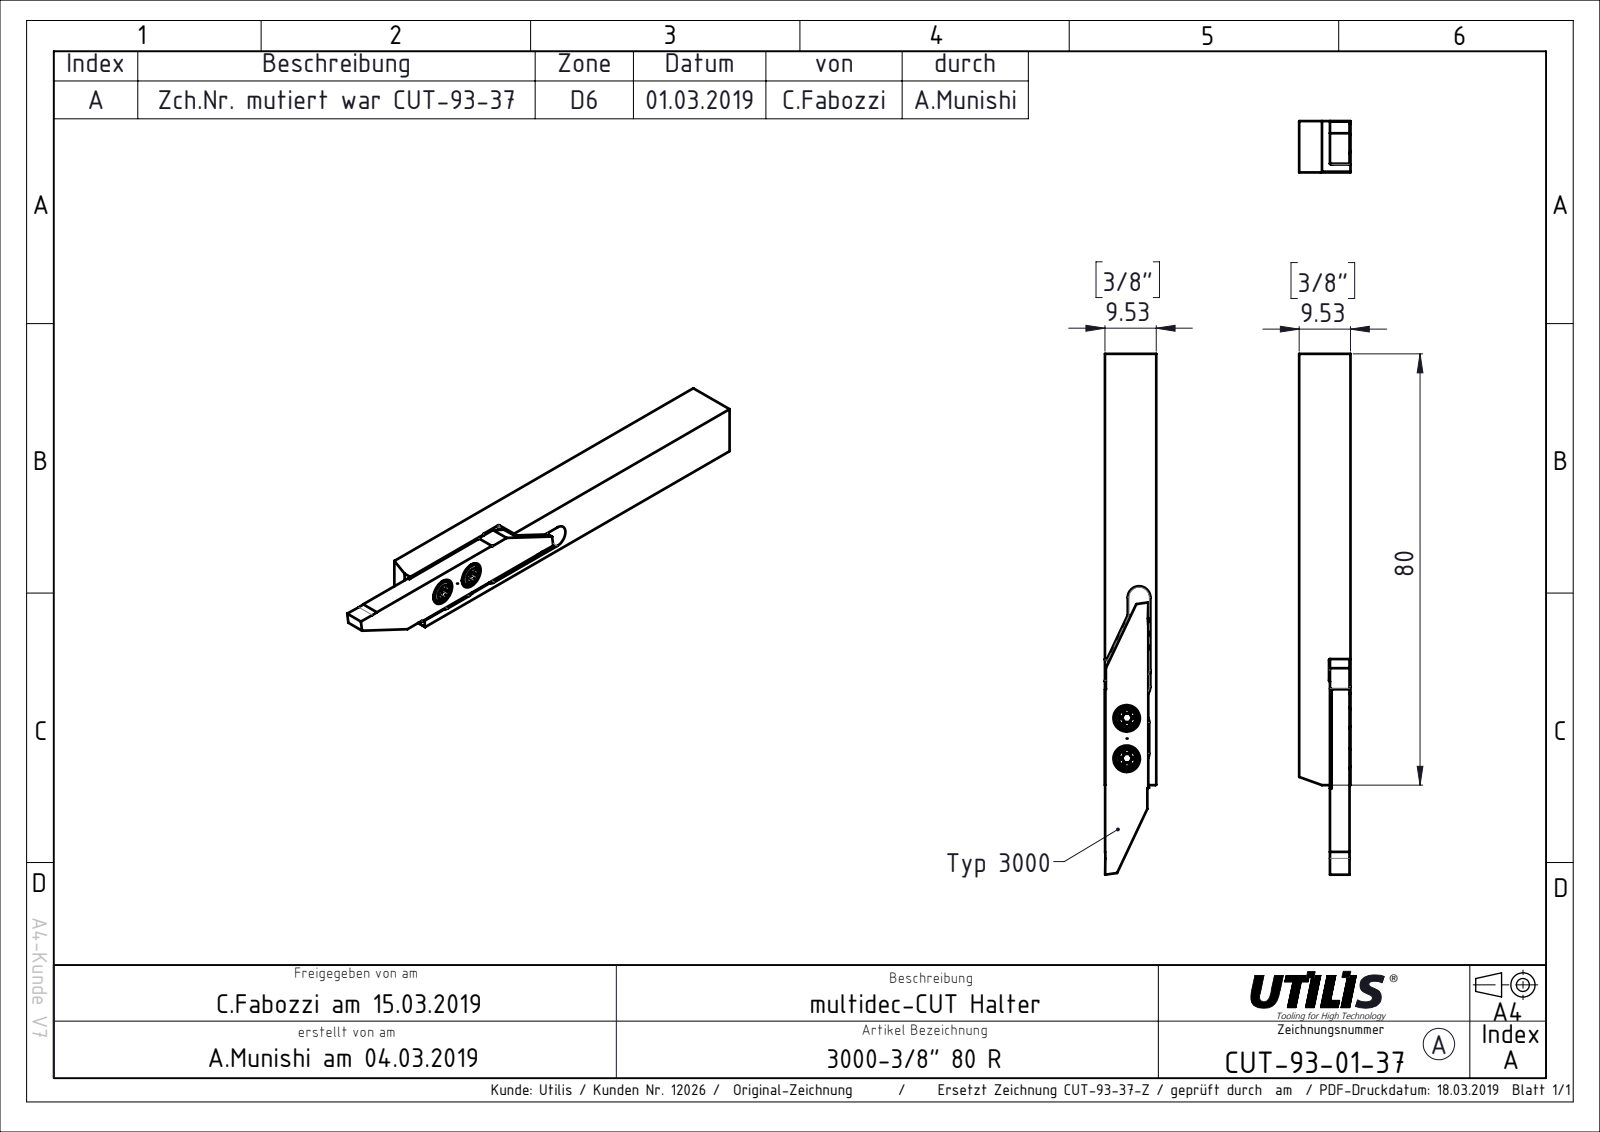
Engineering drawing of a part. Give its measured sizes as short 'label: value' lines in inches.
name: CUT-Vorlage 3000 R+L Lang Kunde; CUT-93-Kunde; CUT-93-37; CUT-Vorlage 3000 R+L Lang Kunde_R-Lang (+1 more)
written by: SolidWorks 2015 (CONFIG_CONTROL_DESIGN)
unit: in
bodies: 2 solids, 55 faces (36 planar, 19 cylindrical, 0 other)
size: 3.799 × 0.375 × 0.375
volume: 0.441 in³; area: 6.884 in²
holes: 2× ⌀0.098, 2× ⌀0.193
rounds: 4× R0.083, 2× R0.006, 2× R0.394
face distances: 0.375, 0.226, 0.15, 0.142, 0.367, 0.06, 0.315, 0.043, 0.018, 0.333
hole spacings: 0.148, 0.295
